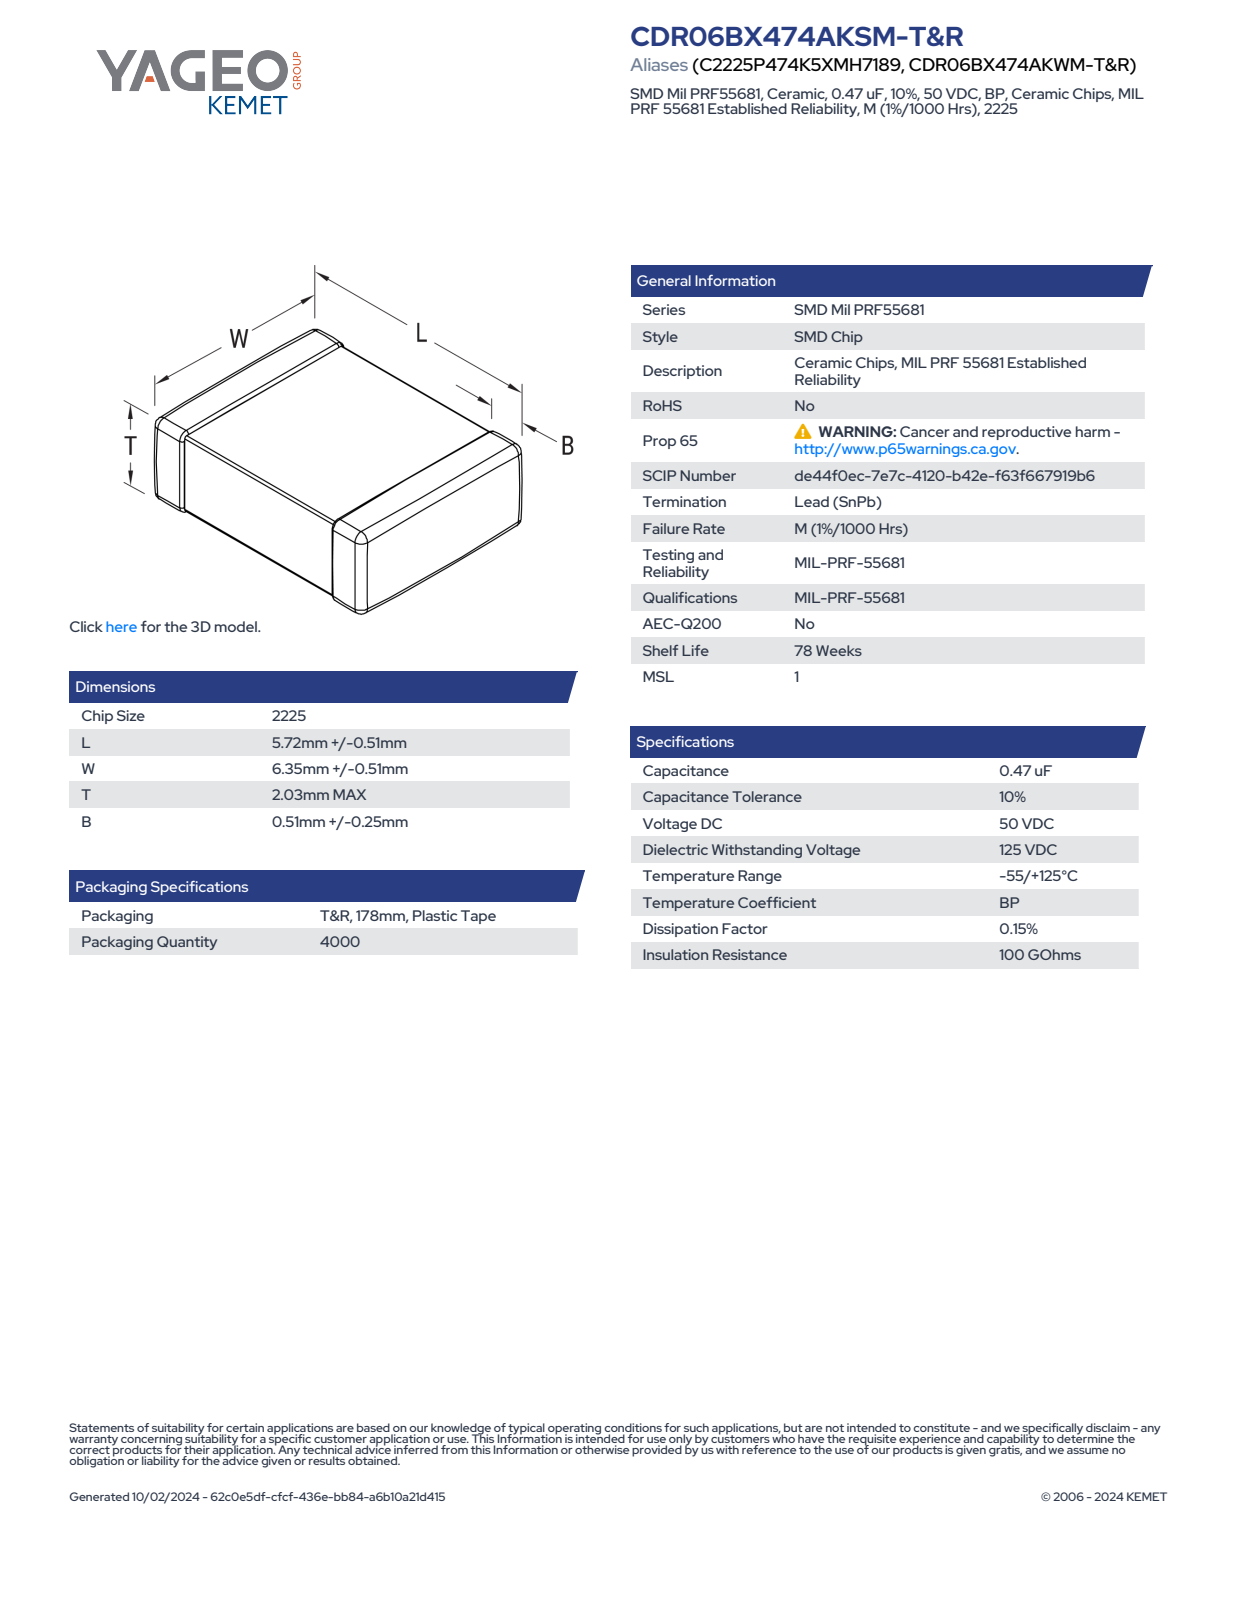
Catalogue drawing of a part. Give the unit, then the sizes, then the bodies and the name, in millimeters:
Units: millimetres
Overall size (bounding box): 6.86 × 6.23 × 2.03
Partial cylindrical surfaces — rounded edges, fillets, slot ends (radius × count): R0.14 ×24
Main face-to-face distances: 1.75, 1.89, 6.23, 6.58, 2.03, 6.72, 6.86, 0.44, 3.49, 3.35
Volume: 75 mm³ · Surface area: 133 mm²
Bodies: 4 solids, 125 faces (71 planar, 38 cylindrical, 16 other)
Part name (STEP PRODUCT): CCS_STDNOS_2225_L6.23W6.86T2.03B0.76
STEP written by: SolidWorks 2021 (AUTOMOTIVE_DESIGN)
